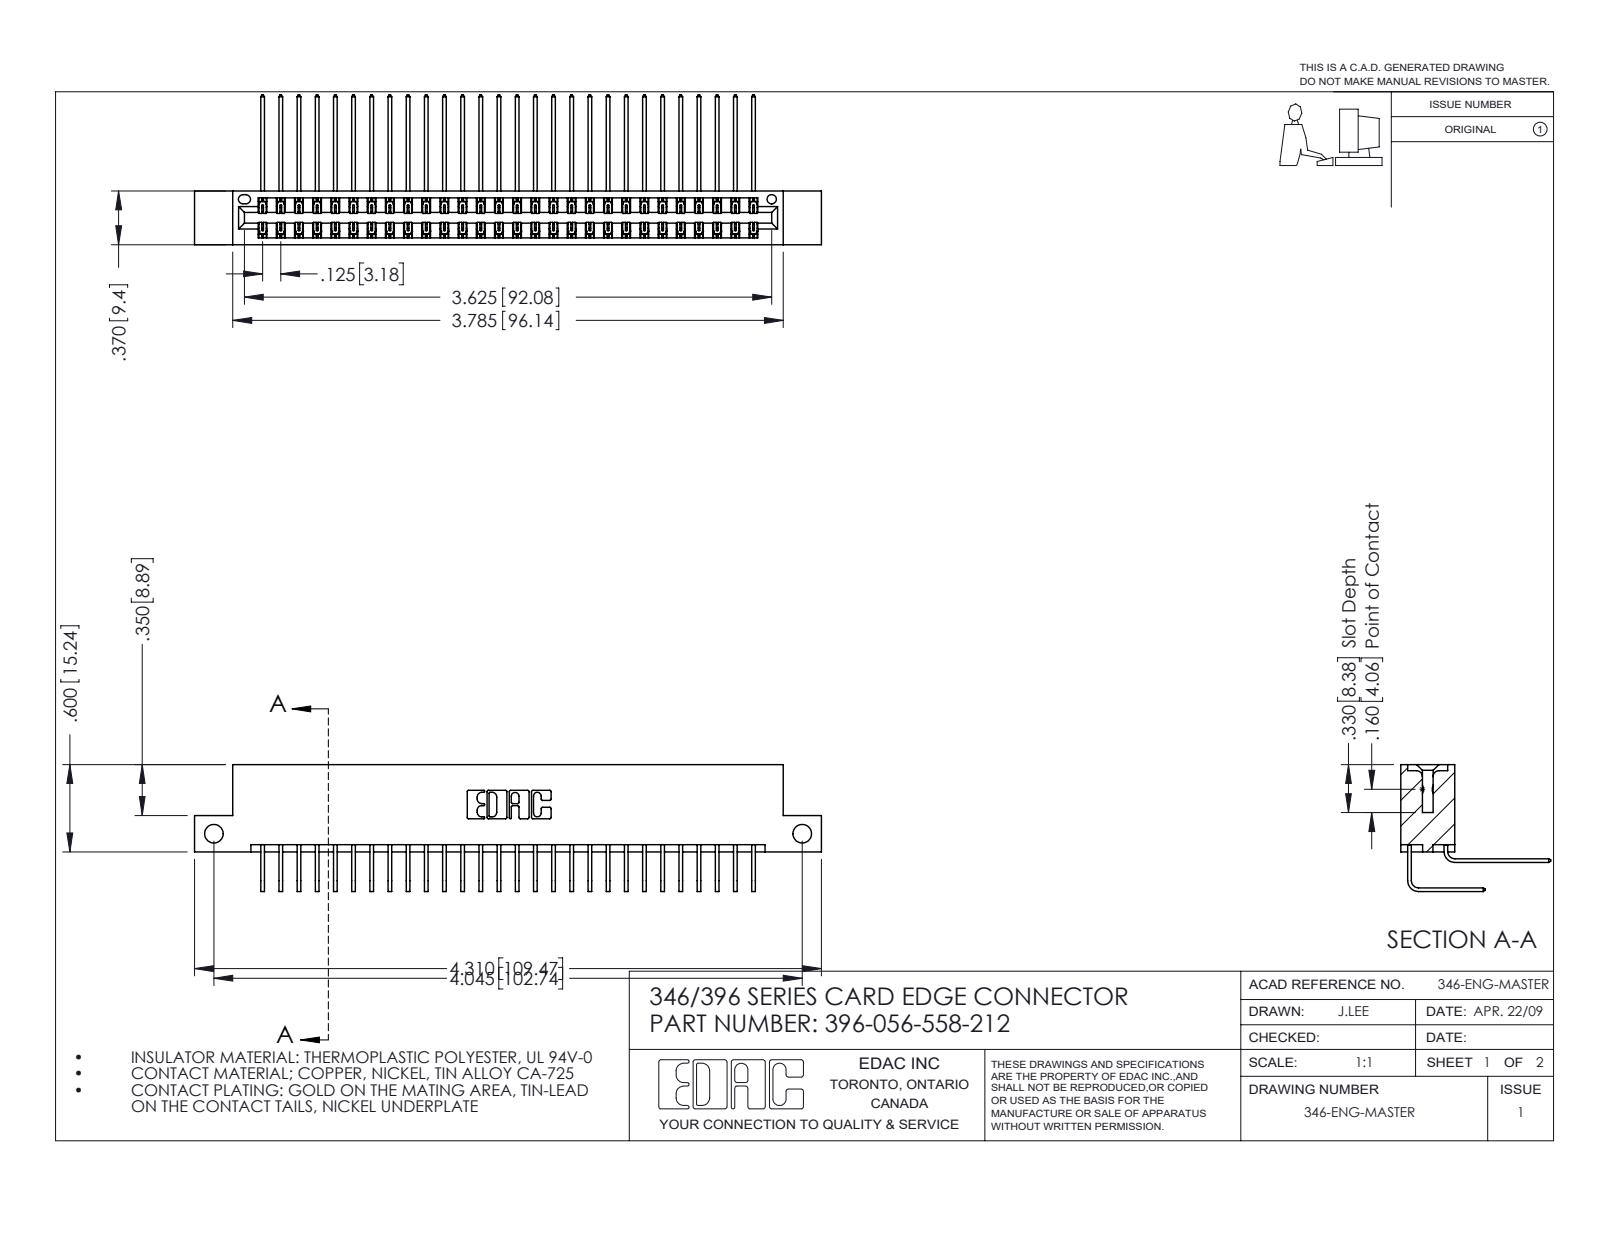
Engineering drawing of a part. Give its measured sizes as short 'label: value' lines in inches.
name: 345-292-001_558 Tail - 2; 346 Part_Flush Mounting Lugs - Side Mount; 396-056-558-212; 345-292-001_558 559 Tail - 1
written by: SolidWorks 2016 (CONFIG_CONTROL_DESIGN)
unit: in
bodies: 57 solids, 3146 faces (2148 planar, 998 cylindrical, 0 other)
size: 4.31 × 1.03 × 0.873
volume: 0.659 in³; area: 24.86 in²
holes: 2× ⌀0.128, 1× ⌀0.064
rounds: 84× R0.006, 22× R0.01, 6× R0.007, 6× R0.031, 3× R0.026, 2× R0.014, 2× R0.022, 2× R0.024
face distances: 0.322, 0.048, 0.025, 0.25, 0.37, 0.298, 0.072, 0.275, 0.148, 0.222
hole spacings: 4.045
